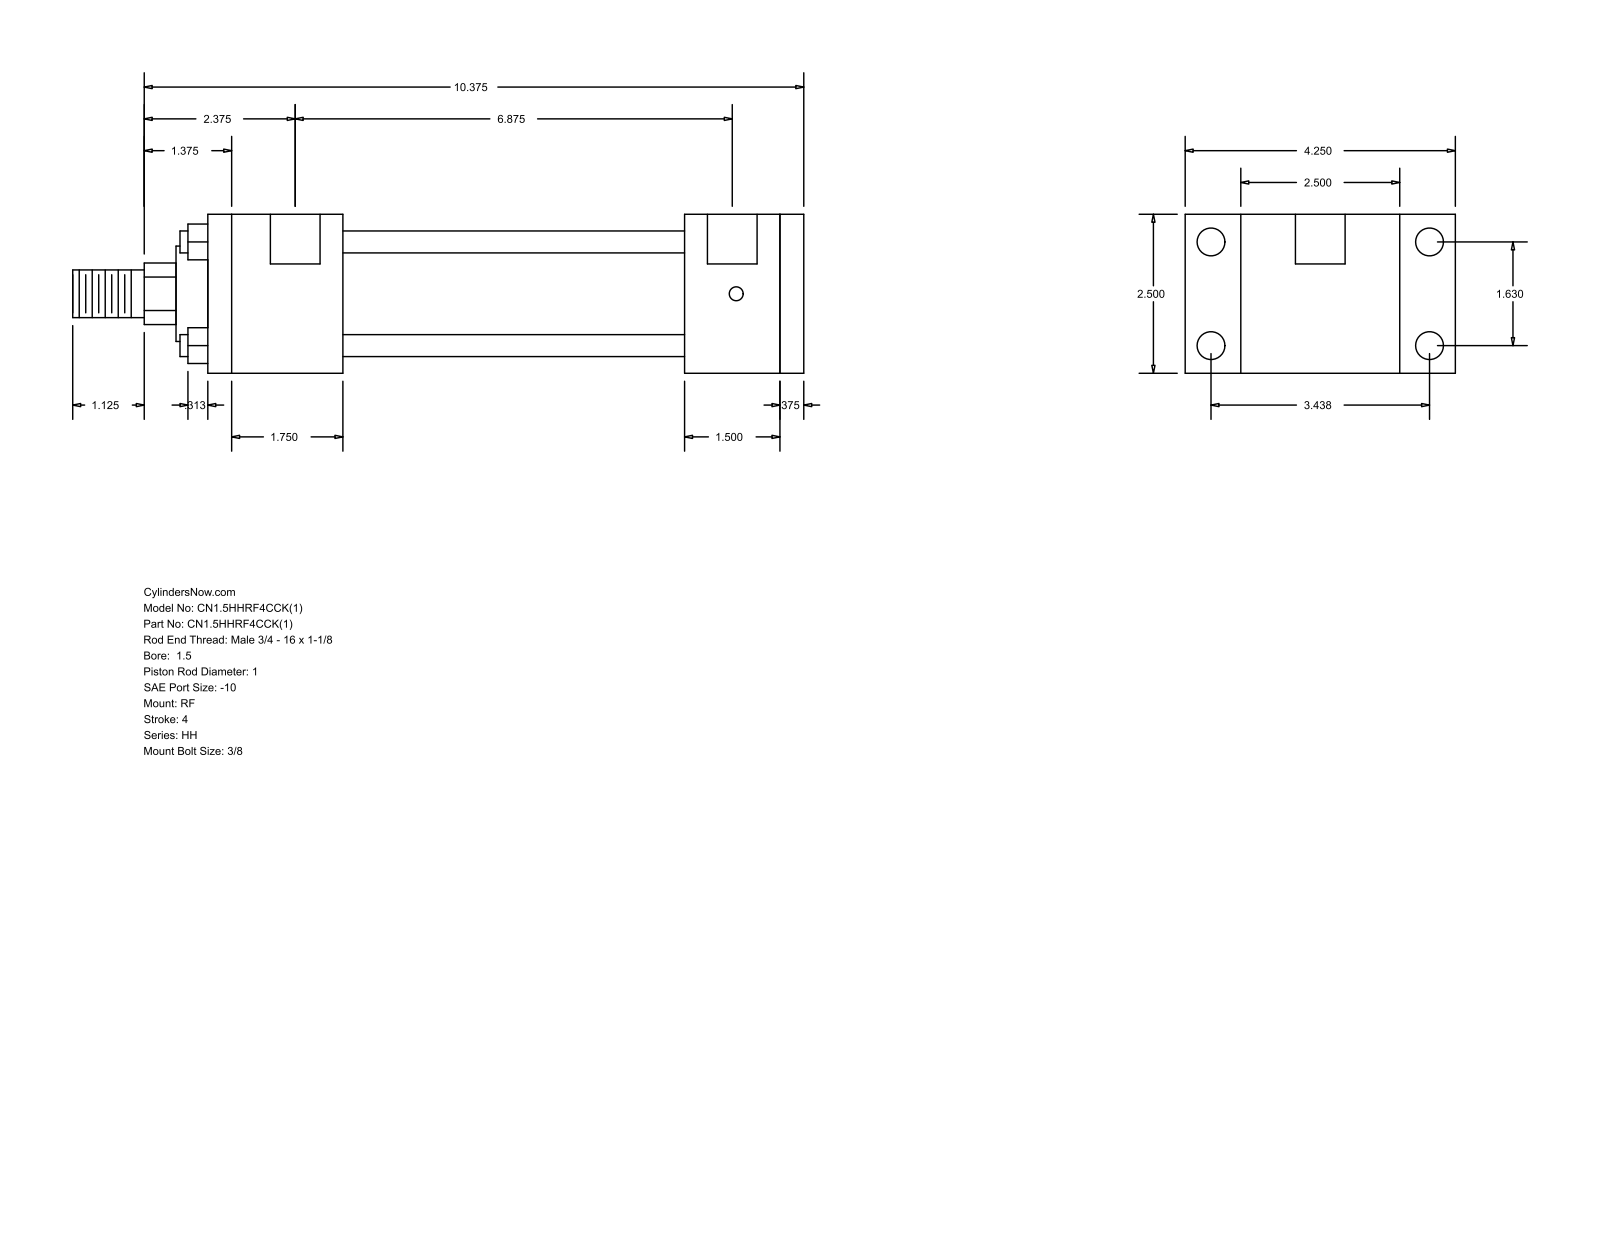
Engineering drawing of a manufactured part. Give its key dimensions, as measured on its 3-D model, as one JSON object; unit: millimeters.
{"part_name": "HH_RF__0150_1", "step_written_by": "GSSL Pune (CONFIG_CONTROL_DESIGN)", "units": "millimeters", "bodies": {"solids": 0, "faces": 92, "planar": 64, "cylindrical": 28, "other": 0}, "overall_size": [292.1, 107.95, 63.5], "round_holes": [[5.56, 4], [11.13, 4], [19.84, 2]], "round_bosses_or_shafts": [[8.76, 4], [44.45, 1], [38.1, 1], [25.4, 1], [19.05, 1]], "partial_cylinders_radius": [[12.29, 1]], "face_to_face_distances": [63.5, 9.52, 38.1, 136.52, 174.62, 184.14, 47.62, 53.98, 190.5, 228.6], "hole_center_spacings": [1.59, 41.4, 87.32, 96.64, 176.21, 177.8, 174.62]}
